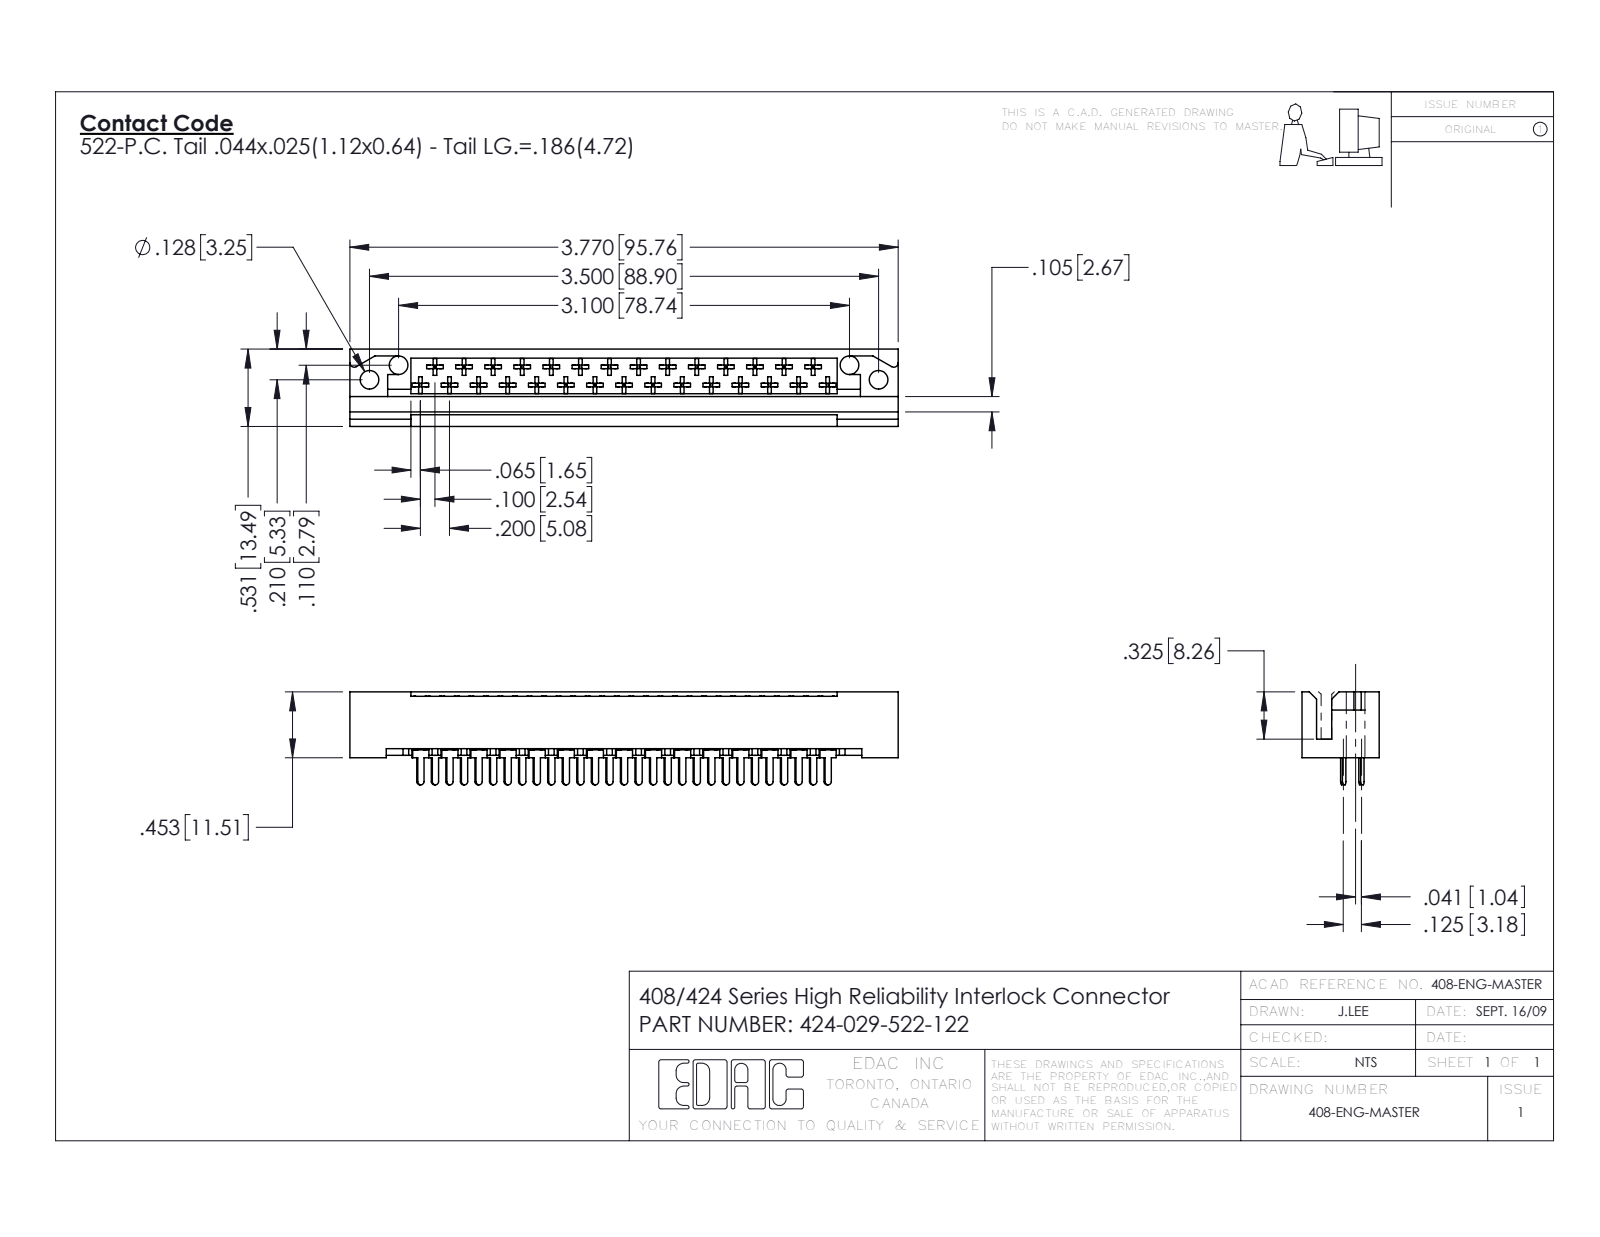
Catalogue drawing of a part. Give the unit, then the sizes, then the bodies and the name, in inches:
Units: inches
Overall size (bounding box): 3.77 × 0.639 × 0.531
Round holes (diameter × count): ⌀0.128 ×4
Partial cylindrical surfaces — rounded edges, fillets, slot ends (radius × count): R0.01 ×174, R0.02 ×31, R0.022 ×29, R0.03 ×2
Main face-to-face distances: 0.1, 0.296, 0.531, 0.025, 0.125, 0.431, 0.259, 0.172, 0.272, 0.235
Hole centre spacings: 0.224, 3.302, 3.1, 3.5
Volume: 0.604 in³ · Surface area: 19.89 in²
Bodies: 30 solids, 1657 faces (1264 planar, 277 cylindrical, 116 other)
Part name (STEP PRODUCT): 424-029-522-122; 424 Part_029; 408-290-001_408-290-122
STEP written by: SolidWorks 2016 (CONFIG_CONTROL_DESIGN)
